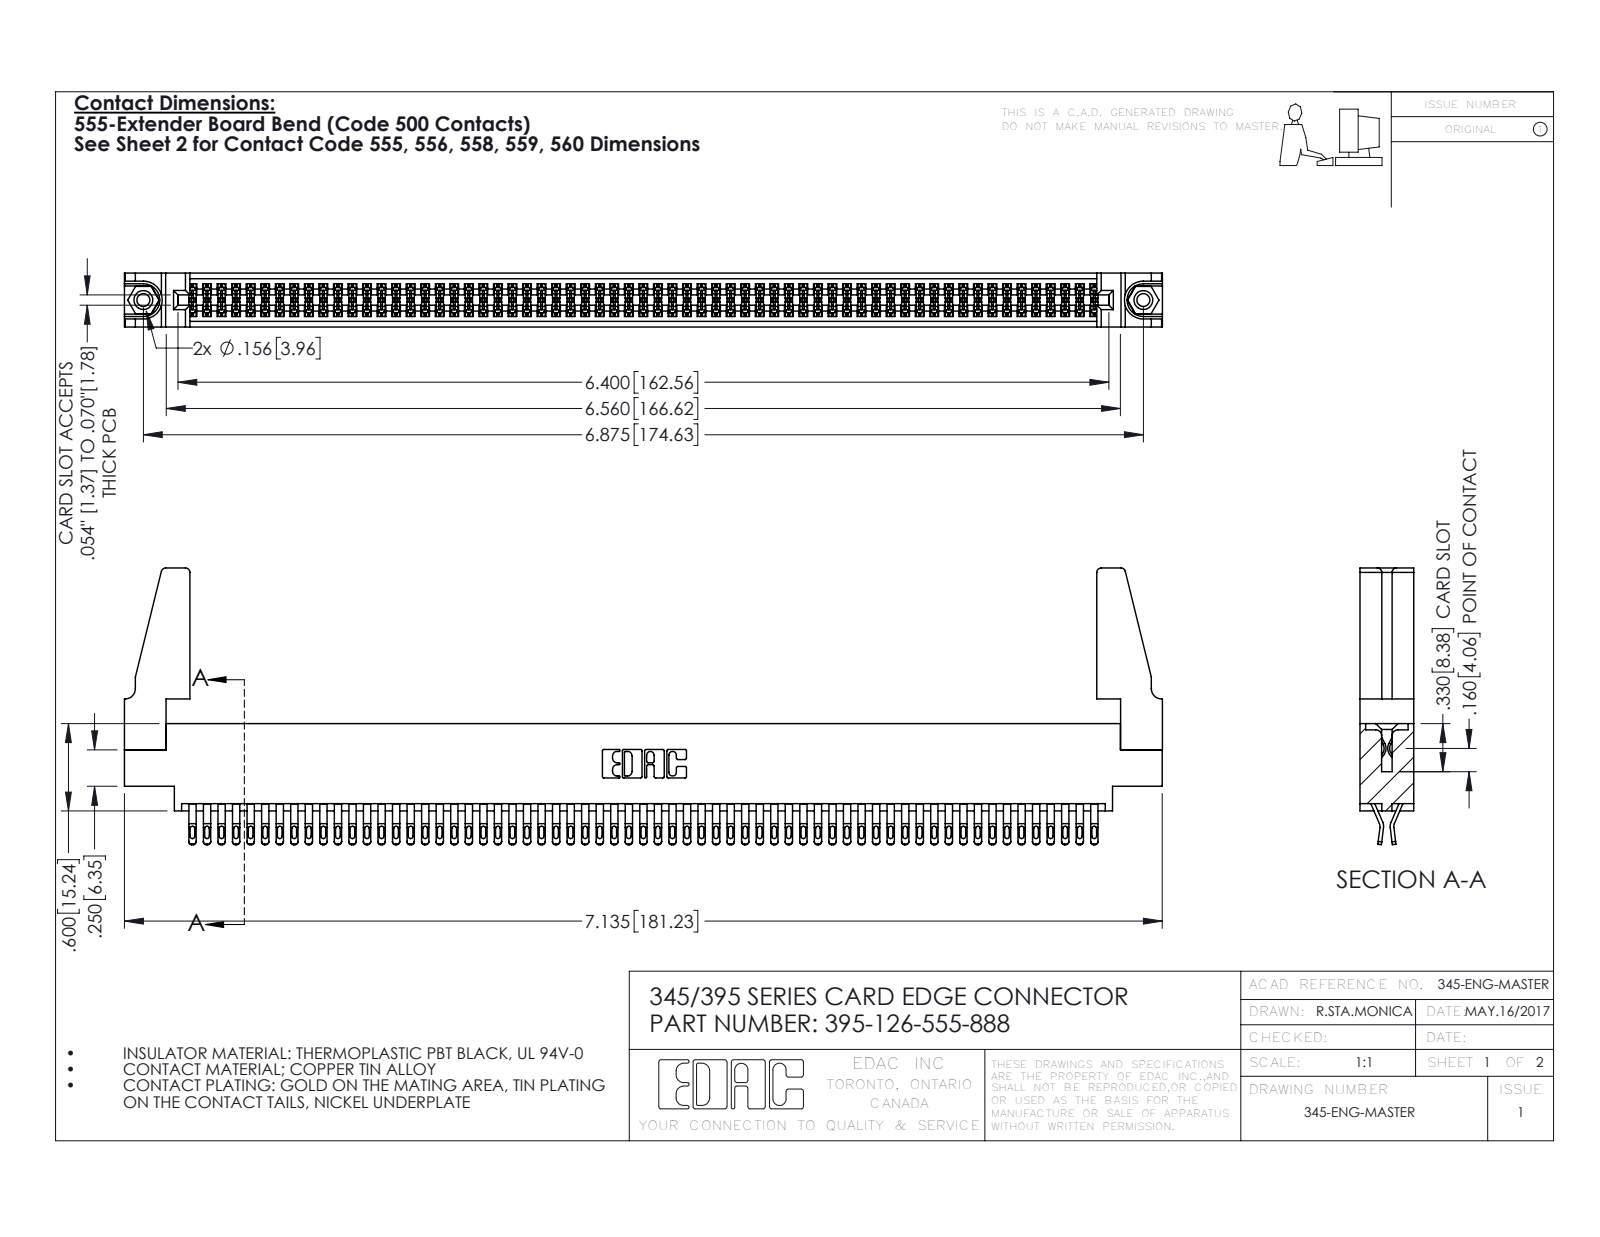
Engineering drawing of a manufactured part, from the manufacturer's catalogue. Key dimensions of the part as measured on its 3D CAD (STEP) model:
Part name (STEP PRODUCT): 345-220-078_345-220-088; 345 Part_0.170 Offset - 0.156 Dia-TH; 345-292-001_555 Tail; 345-250-001_345-250-001-102 (+1 more)
STEP written by: SolidWorks 2016 (CONFIG_CONTROL_DESIGN)
Units: inches
Bodies: 131 solids, 7310 faces (4062 planar, 3232 cylindrical, 16 other)
Overall size (bounding box): 7.136 × 1.902 × 0.37
Volume: 1.3 in³ · Surface area: 49.03 in²
Round holes (diameter × count): ⌀0.089 ×2, ⌀0.125 ×2, ⌀0.156 ×2, ⌀0.064 ×1
Round bosses / shafts (diameter × count): ⌀0.155 ×2
Partial cylindrical surfaces — rounded edges, fillets, slot ends (radius × count): R0.016 ×315, R0.02 ×252, R0.006 ×189, R0.01 ×22, R0.03 ×8, R0.007 ×6, R0.031 ×6, R0.026 ×3
Main face-to-face distances: 0.072, 0.298, 0.37, 0.025, 0.2, 0.098, 0.272, 0.225, 0.175, 0.149
Hole centre spacings: 0.27, 6.639, 6.875
